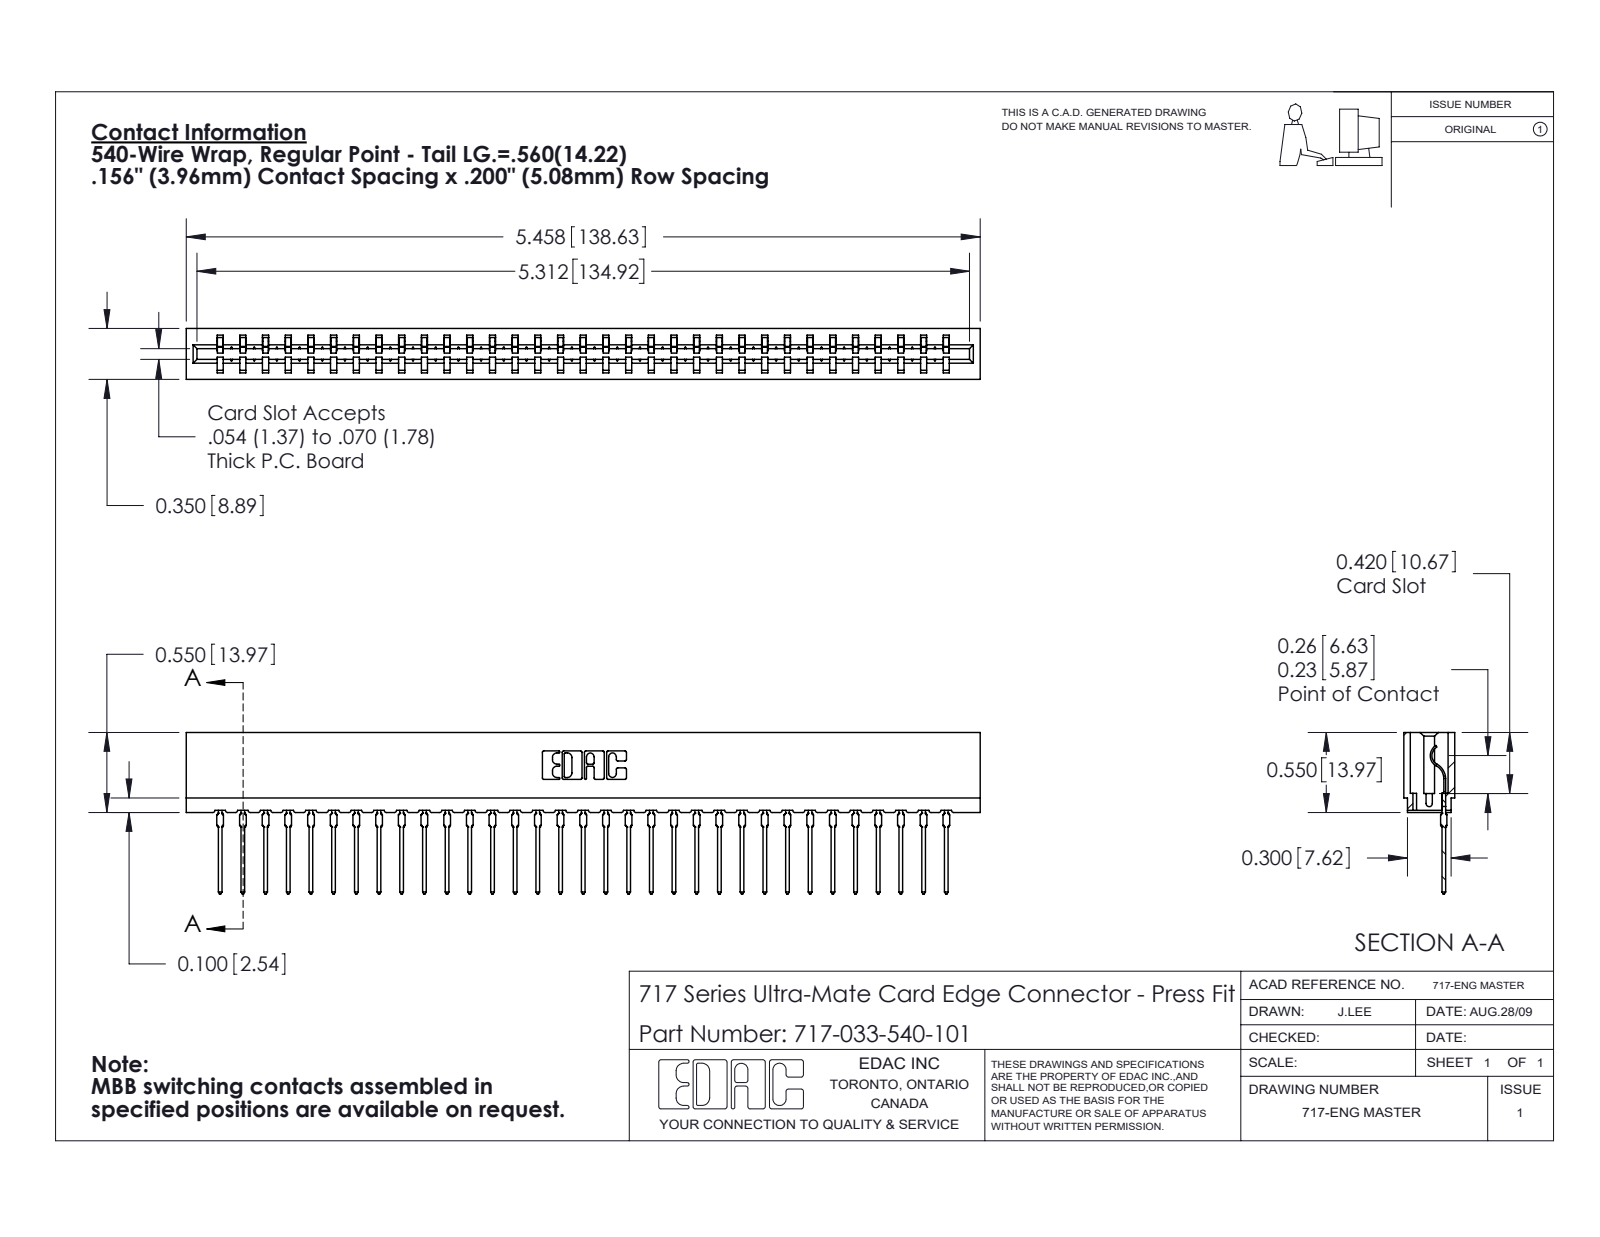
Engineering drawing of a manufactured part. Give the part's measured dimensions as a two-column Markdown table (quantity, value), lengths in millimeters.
| quantity | value |
| --- | --- |
| part name | 717-033-540-101; 717 Part_Insulator Option - 06; 745-292-001_540 |
| STEP written by | SolidWorks 2020 (CONFIG_CONTROL_DESIGN) |
| units | millimeters |
| bodies | 34 solids, 3823 faces (2298 planar, 667 cylindrical, 858 other) |
| overall size | 138.6 × 28.2 × 8.9 |
| volume | 11 800 mm³ |
| surface area | 16 890 mm² |
| partial cylindrical surfaces (radius × count) | 0.4 × 66, 0.5 × 66, 0.3 × 22, 0.2 × 6, 0.8 × 6, 0.1 × 4, 0.3 × 4, 0.7 × 3 |
| main face-to-face distances | 5.4, 3.5, 8.9, 1.9, 1.6, 7.3, 1.9, 3.8, 1.1, 7.7 |
